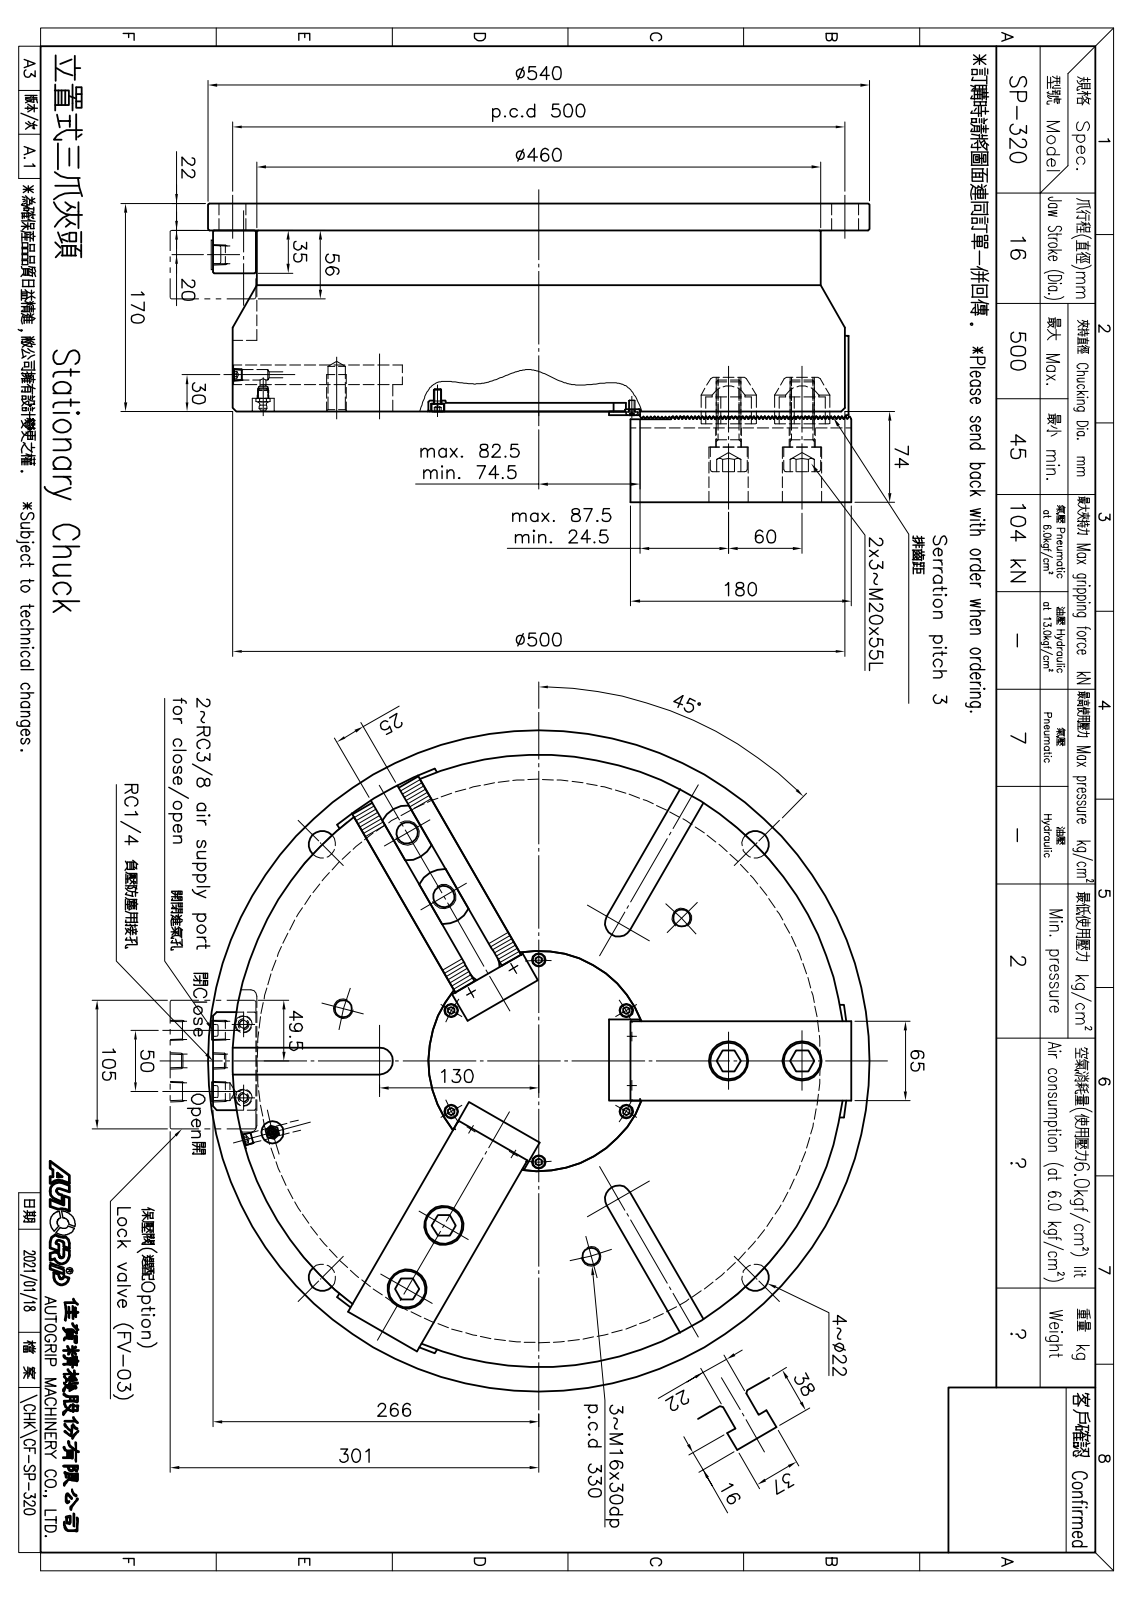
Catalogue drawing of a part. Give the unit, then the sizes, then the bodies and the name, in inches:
Units: inches
Overall size (bounding box): 21.26 × 21.26 × 9.614
Round holes (diameter × count): ⌀0.689 ×12, ⌀0.551 ×9, ⌀0.197 ×7, ⌀0.165 ×6, ⌀0.26 ×6, ⌀0.433 ×6, ⌀0.827 ×6, ⌀1.26 ×6, ⌀0.866 ×4, ⌀0.13 ×3, ⌀0.177 ×3, ⌀0.268 ×2
Round bosses / shafts (diameter × count): ⌀1.181 ×6, ⌀0.787 ×6, ⌀0.394 ×6, ⌀0.236 ×6, ⌀0.315 ×5, ⌀0.157 ×3, ⌀0.827 ×2, ⌀0.591 ×2
Partial cylindrical surfaces — rounded edges, fillets, slot ends (radius × count): R0.004 ×318, R0.492 ×9, R0.886 ×6, R0.433 ×3, R0.728 ×3, R11.024 ×3, R0.197 ×2, R2.992 ×1
Main face-to-face distances: 0.866, 5.827, 6.693, 0.059, 2.008, 4.685, 3.819, 2.5, 2.559, 0.787
Hole centre spacings: 9.843, 3.248, 8.687, 11.807, 5.626, 6.594, 11.983, 0.984
Volume: 2 087 in³ · Surface area: 2 965 in²
Bodies: 43 solids, 3977 faces (3021 planar, 804 cylindrical, 152 other)
Part name (STEP PRODUCT): CF-SP-320-06000; 圓頭內六角螺栓_M6x12; SJ-21; 錐平頭六角孔螺栓_M4x10 (+8 more)
STEP written by: SolidWorks 2020 (CONFIG_CONTROL_DESIGN)
